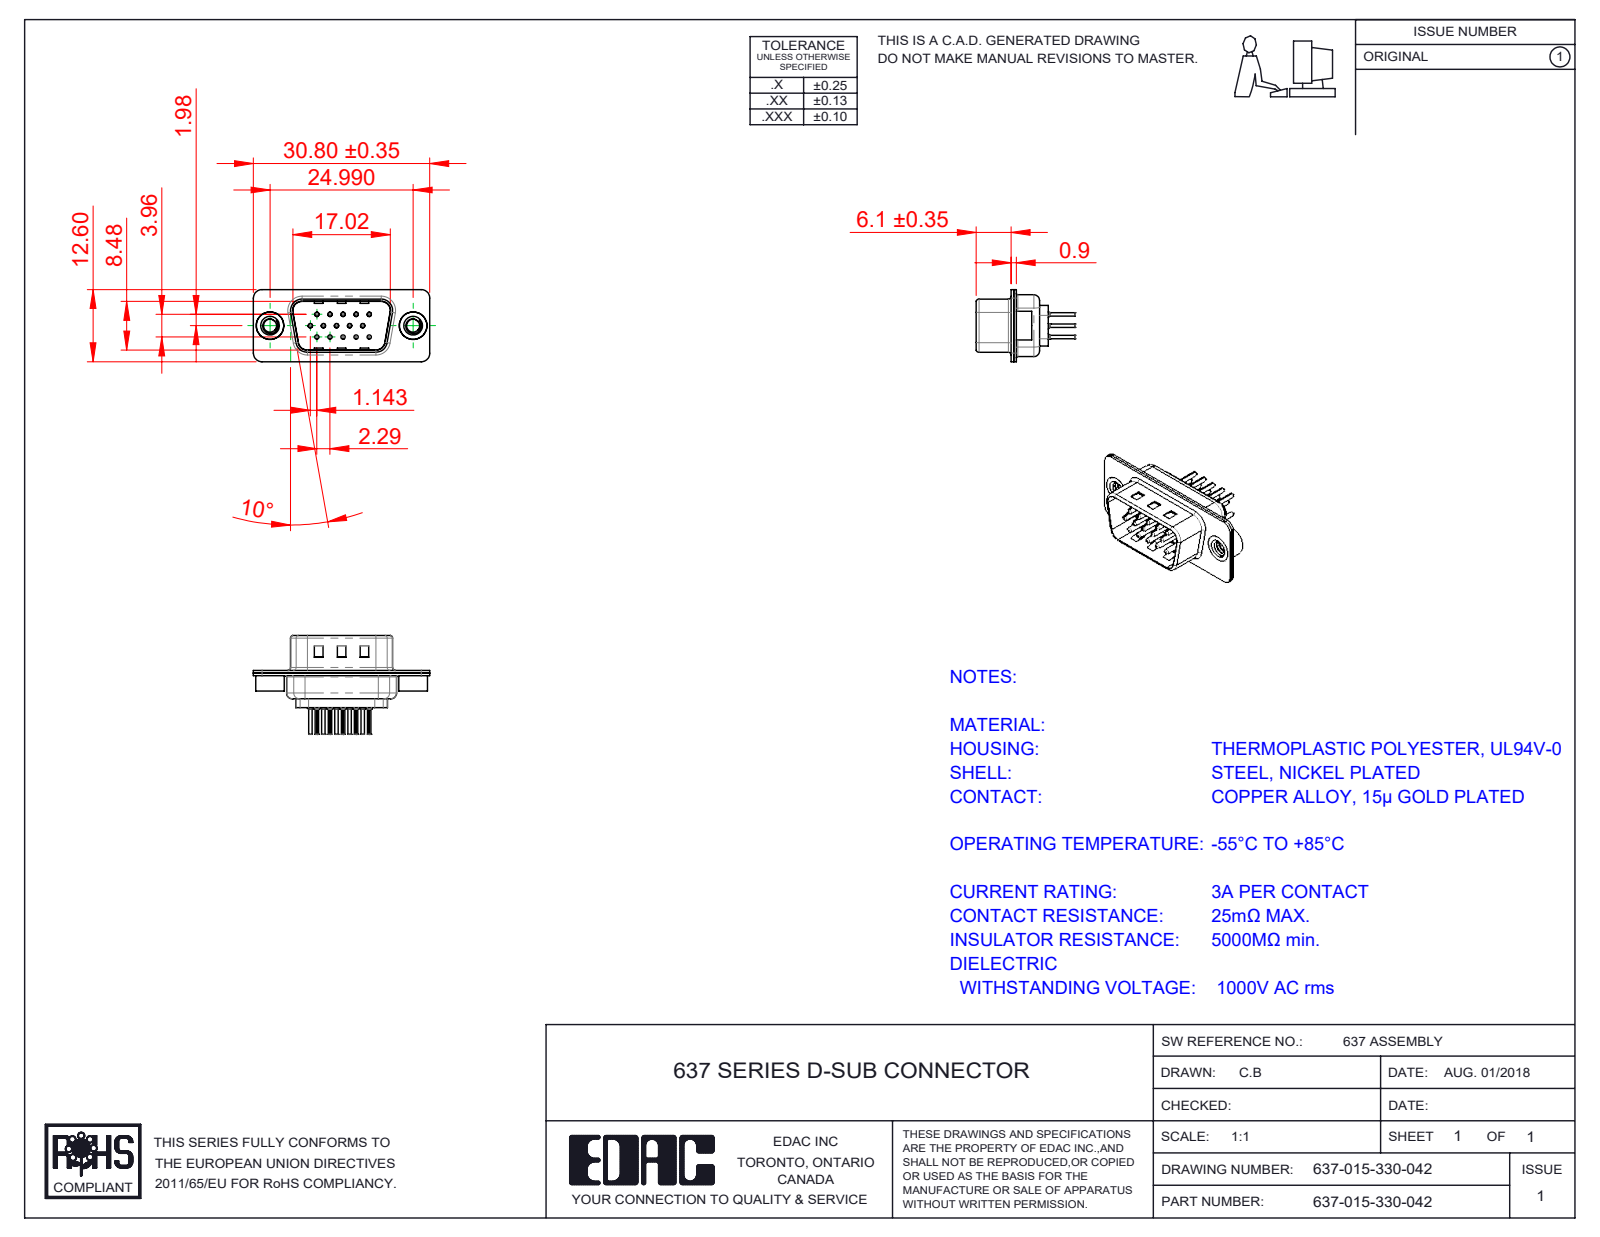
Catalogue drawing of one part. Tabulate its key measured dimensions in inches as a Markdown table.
| quantity | value |
| --- | --- |
| part name | 637 4-40 Threaded Rivet; 637 Shell Front_15 Contacts; 637 Contact Row 2_30; 637 Contact Row 1_30 (+4 more) |
| STEP written by | SolidWorks 2020 (CONFIG_CONTROL_DESIGN) |
| units | inches |
| bodies | 20 solids, 1804 faces (467 planar, 684 cylindrical, 653 other) |
| overall size | 1.213 × 0.679 × 0.496 |
| volume | 0.08 in³ |
| surface area | 7.203 in² |
| round holes (diameter × count) | 0.008 × 15, 0.014 × 15, 0.043 × 15, 0.063 × 15, 0.089 × 2, 0.157 × 2, 0.189 × 2 |
| round bosses / shafts (diameter × count) | 0.079 × 15, 0.059 × 15, 0.03 × 15, 0.024 × 15, 0.197 × 2, 0.193 × 2 |
| partial cylindrical surfaces (radius × count) | 0.004 × 30, 0.059 × 16, 0.079 × 12, 0.02 × 8, 0.01 × 4, 0.022 × 4, 0.028 × 4, 0.037 × 4 |
| main face-to-face distances | 0.018, 0.035, 0.016, 0.028, 0.35, 0.334, 0.041, 0.012, 0.179, 0.046 |
| hole center spacings | 0.156, 0.09, 0.18, 0.09, 0.238, 0.27, 0.312, 0.238 |
